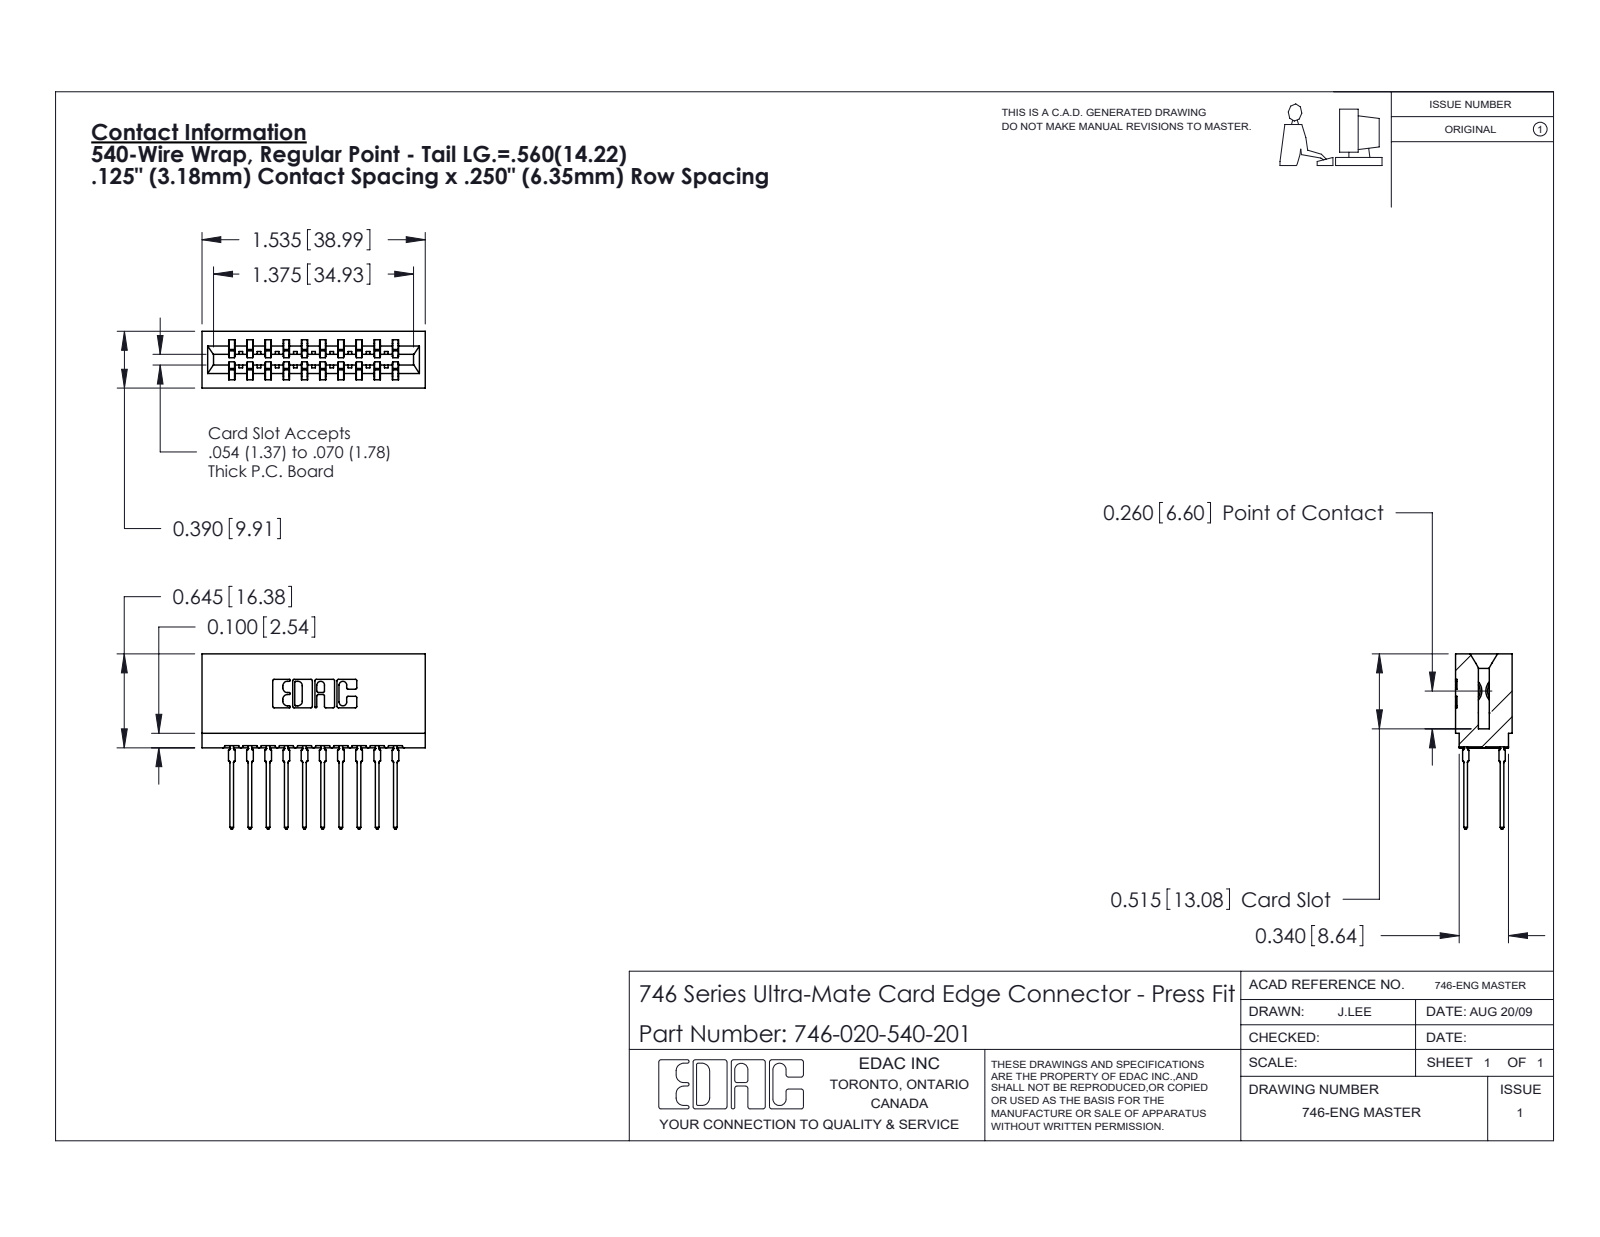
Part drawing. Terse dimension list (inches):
name: 746-292-001_540; 746-020-540-201; 746 Part_.515 Slot Depth - 01
written by: SolidWorks 2020 (CONFIG_CONTROL_DESIGN)
unit: in
bodies: 21 solids, 1887 faces (975 planar, 392 cylindrical, 520 other)
size: 1.535 × 1.204 × 0.39
volume: 0.271 in³; area: 10.51 in²
rounds: 40× R0.021, 22× R0.01, 11× R0.015, 8× R0.005, 8× R0.011, 6× R0.007, 6× R0.031, 3× R0.026
face distances: 0.25, 0.333, 0.057, 0.5, 0.125, 0.042, 0.375, 0.208, 0.125, 0.083
